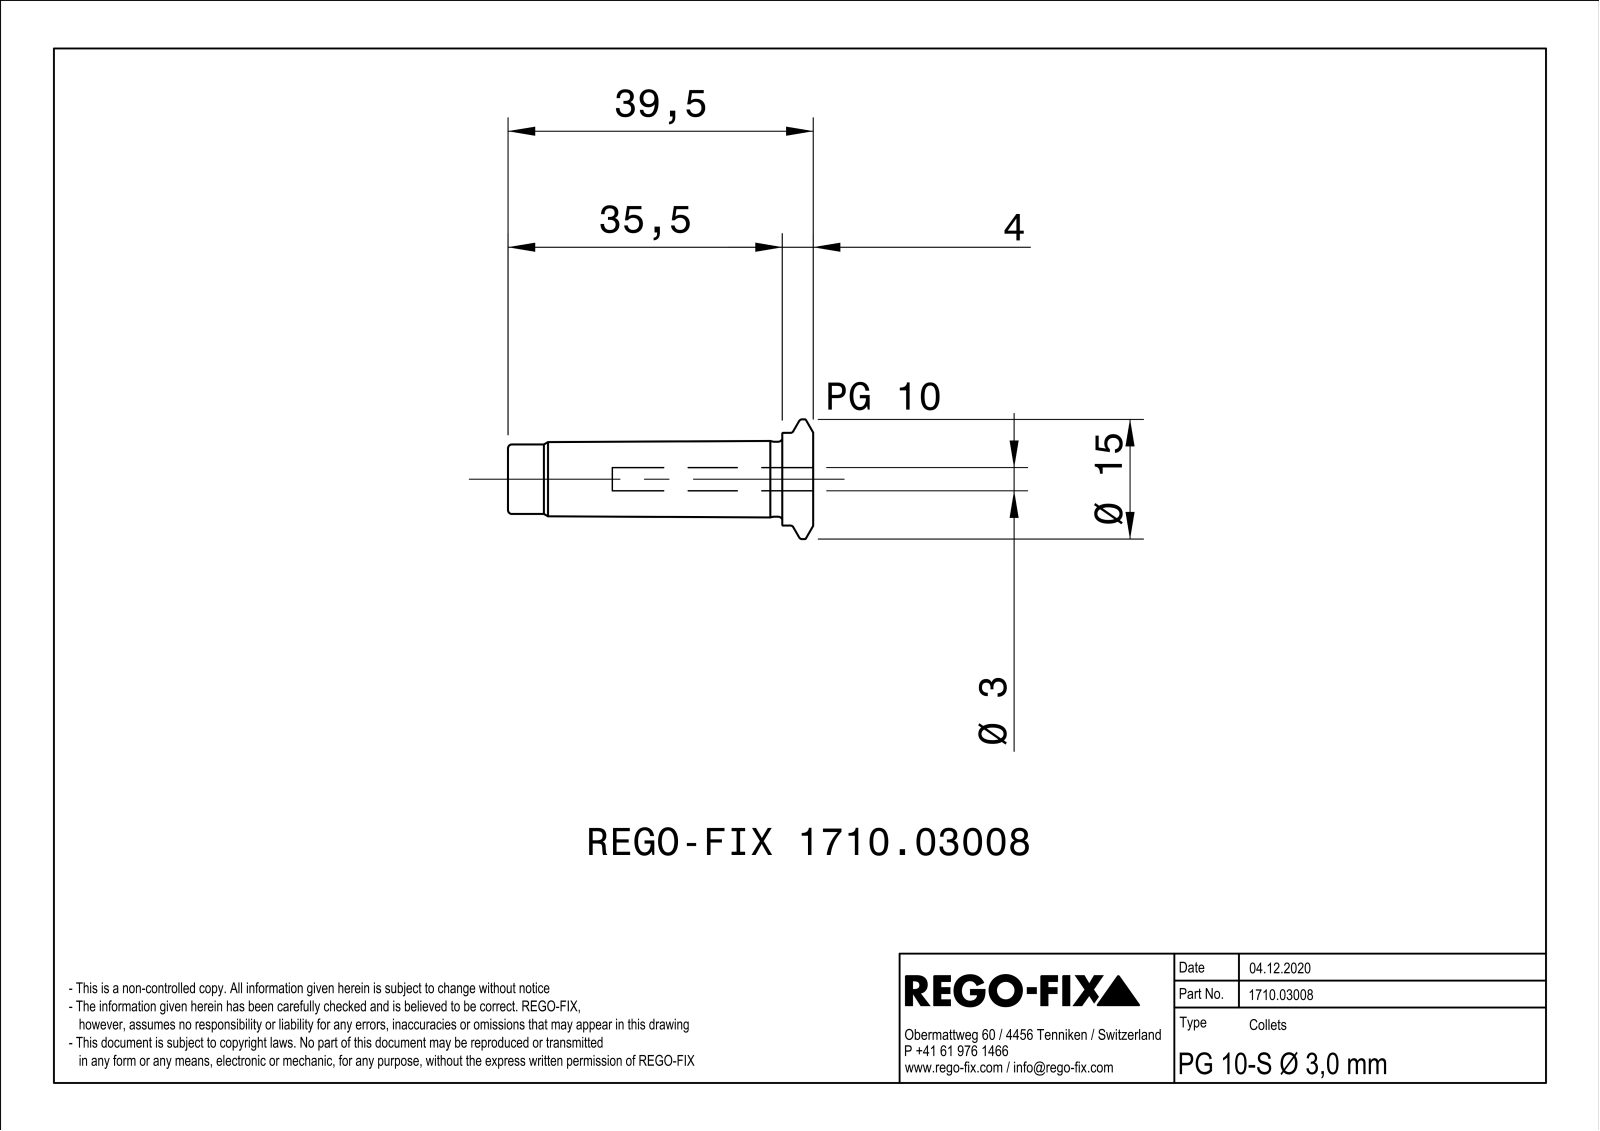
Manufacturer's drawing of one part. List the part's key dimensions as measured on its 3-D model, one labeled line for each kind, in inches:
Part name (STEP PRODUCT): NOCUT
STEP written by: SIEMENS PLM Software Solid Edge ST10 (AUTOMOTIVE_DESIGN)
Units: inches
Bodies: 0 solids, 61 faces (11 planar, 18 cylindrical, 32 other)
Overall size (bounding box): 1.555 × 0.61 × 0.61
Round holes (diameter × count): ⌀0.118 ×1, ⌀0.244 ×1
Round bosses / shafts (diameter × count): ⌀0.61 ×1, ⌀0.472 ×1, ⌀0.382 ×1, ⌀0.354 ×1
Partial cylindrical surfaces — rounded edges, fillets, slot ends (radius × count): R0.016 ×6
Main face-to-face distances: 0.031, 1.555, 0.157, 1.398
